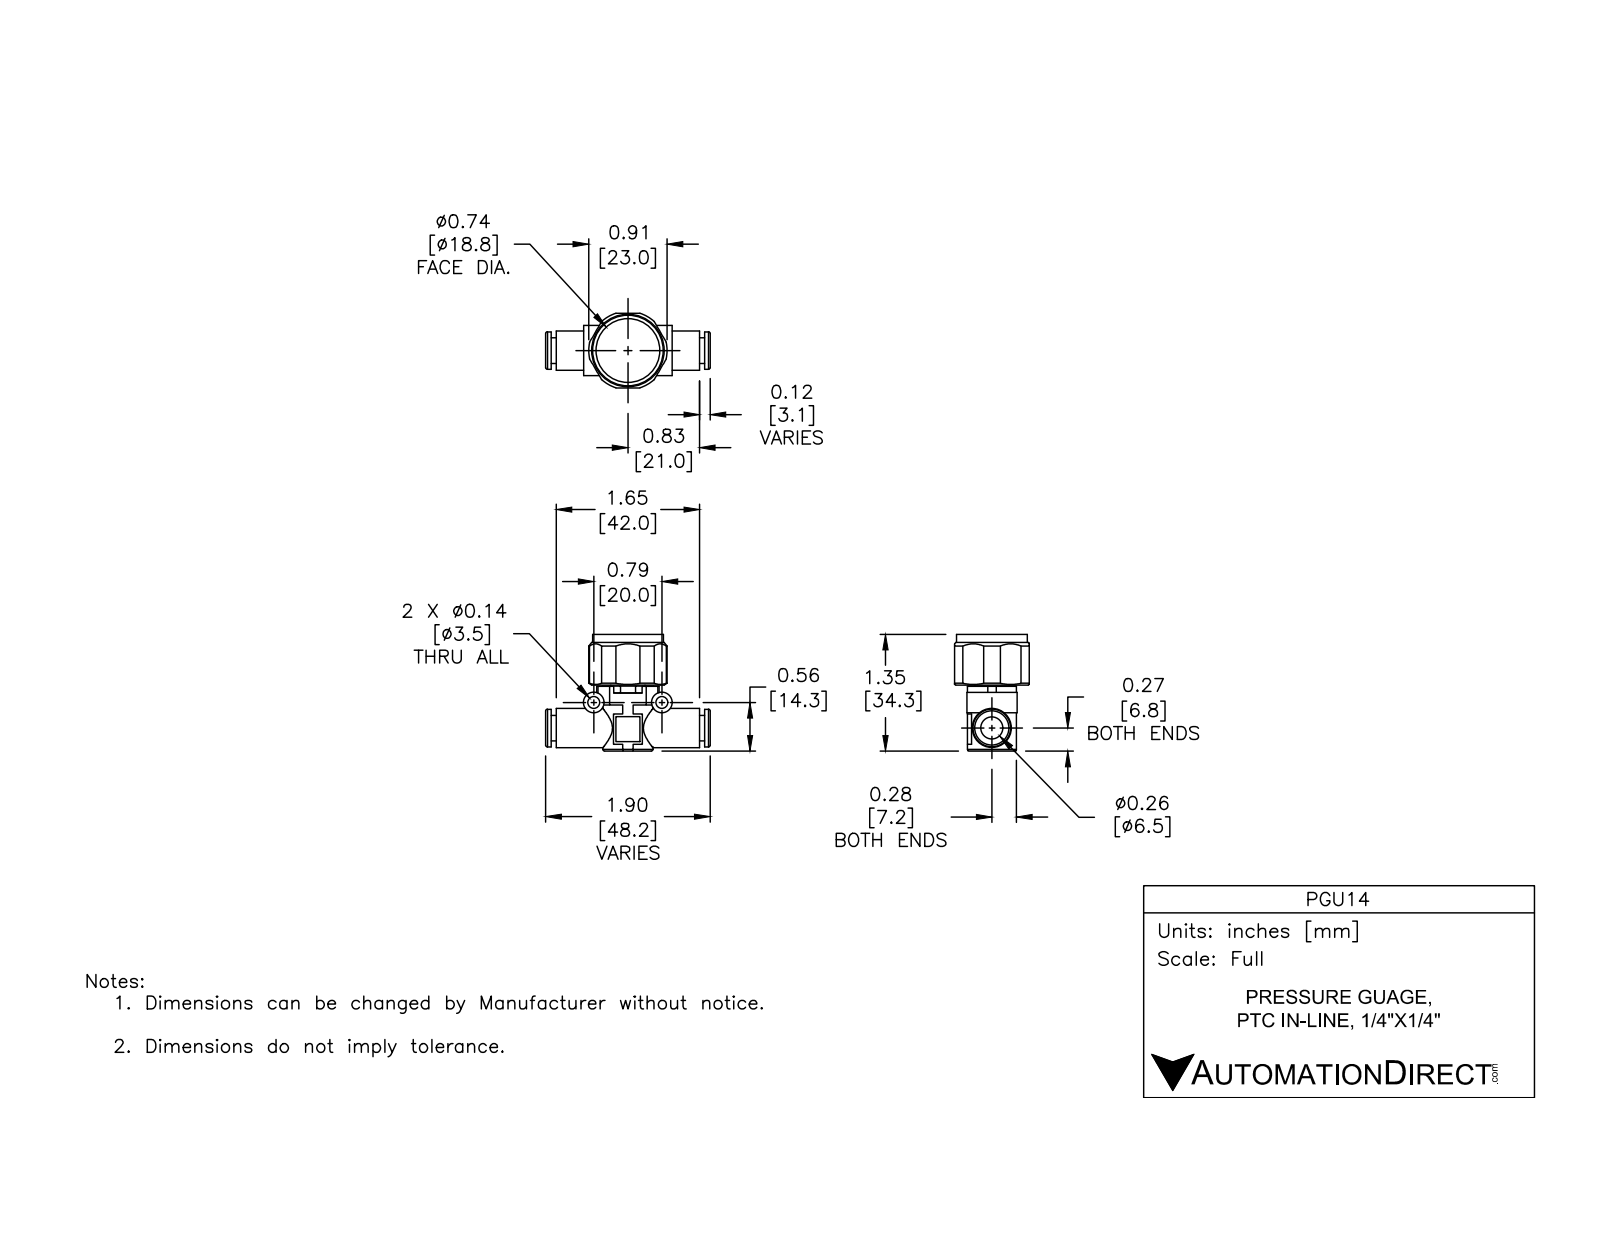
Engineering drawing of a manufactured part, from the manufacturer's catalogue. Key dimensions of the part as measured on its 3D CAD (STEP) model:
Part name (STEP PRODUCT): PGU14
STEP written by: SolidWorks 2015 (CONFIG_CONTROL_DESIGN)
Units: millimetres
Bodies: 67 solids, 611 faces (429 planar, 67 cylindrical, 115 other)
Overall size (bounding box): 48.2 × 34.25 × 21.9
Volume: 10 327 mm³ · Surface area: 9 158 mm²
Round holes (diameter × count): ⌀3.5 ×2, ⌀6.5 ×1, ⌀7.75 ×1, ⌀18.75 ×1, ⌀19.98 ×1, ⌀20.75 ×1
Round bosses / shafts (diameter × count): ⌀6 ×2, ⌀15 ×1, ⌀14.65 ×1, ⌀11.5 ×1, ⌀11 ×1, ⌀10 ×1, ⌀7.5 ×1, ⌀3.5 ×1
Partial cylindrical surfaces — rounded edges, fillets, slot ends (radius × count): R0.5 ×2, R2.5 ×2, R3.56 ×2, R1 ×1, R4.25 ×1, R7.25 ×1, R11.5 ×1
Main face-to-face distances: 1.5, 4.4, 2, 0.5, 2.4, 2.9, 8.5, 10.5, 10, 12.9
Hole centre spacings: 20
